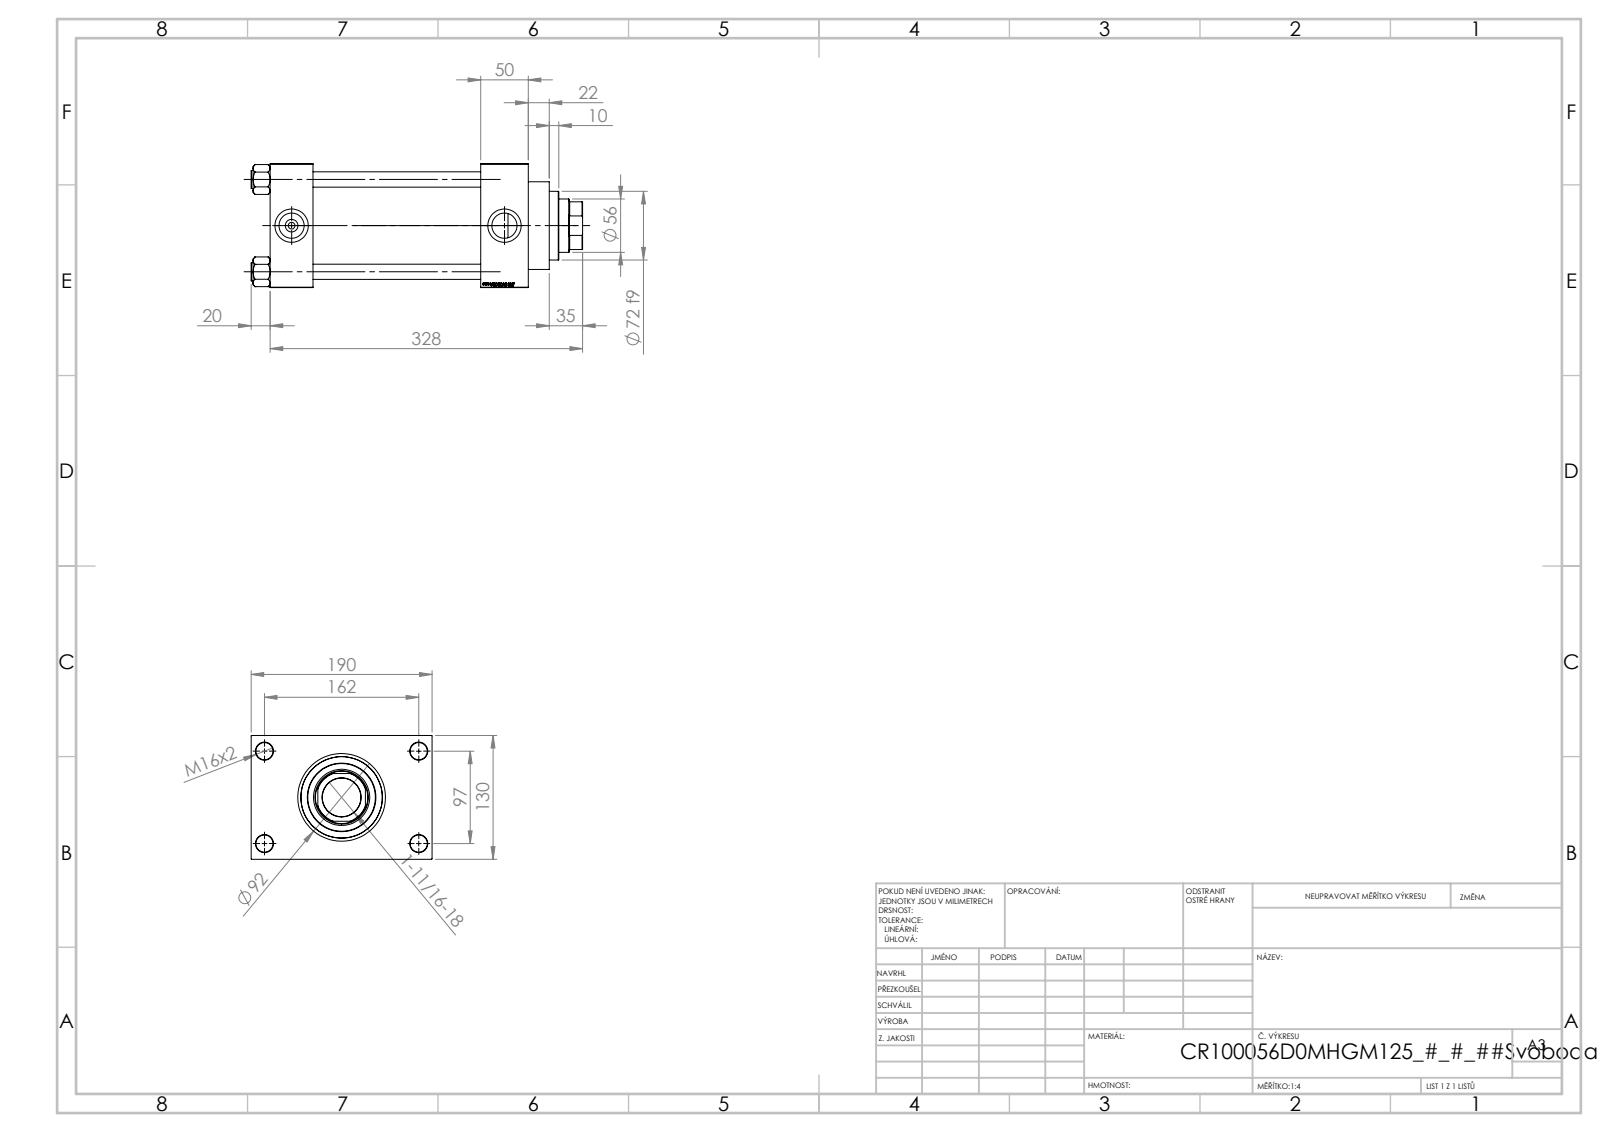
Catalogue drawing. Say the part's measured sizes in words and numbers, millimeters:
The part is named "V215CR_VCP_D; V215CR_D_TYCINKA; V215_VC_A; NUT_M5_D (+1 more)". Its 3-D file was written by "SolidWorks 2019 (CONFIG_CONTROL_DESIGN)". It is 11 solids with 1151 faces: 545 planar, 88 cylindrical and 518 other. Overall it measures 348 by 190 by 130 millimeters. Its volume is 3 073 000 cubic millimeters and its surface area 469 900 square millimeters. Round holes: 4 of diameter 16, 4 of diameter 18, 2 of diameter 7, 2 of diameter 26.44, 2 of diameter 35, 1 of diameter 40.5, 1 of diameter 56, 1 of diameter 59, 1 of diameter 76, 1 of diameter 85.5, 1 of diameter 100. Round bosses or shafts: 4 of diameter 19, 1 of diameter 106, 1 of diameter 92, 1 of diameter 72. Partial cylindrical surfaces (rounded edges, fillets, slot ends): 1 of radius 27. The main face-to-face distances are 130, 50, 45, 221, 176, 271, 226, 30, 160, 190. The hole center spacings are 32.55, 68.52, 94.41, 96.9, 102.27, 129.45, 161.73, 97.
